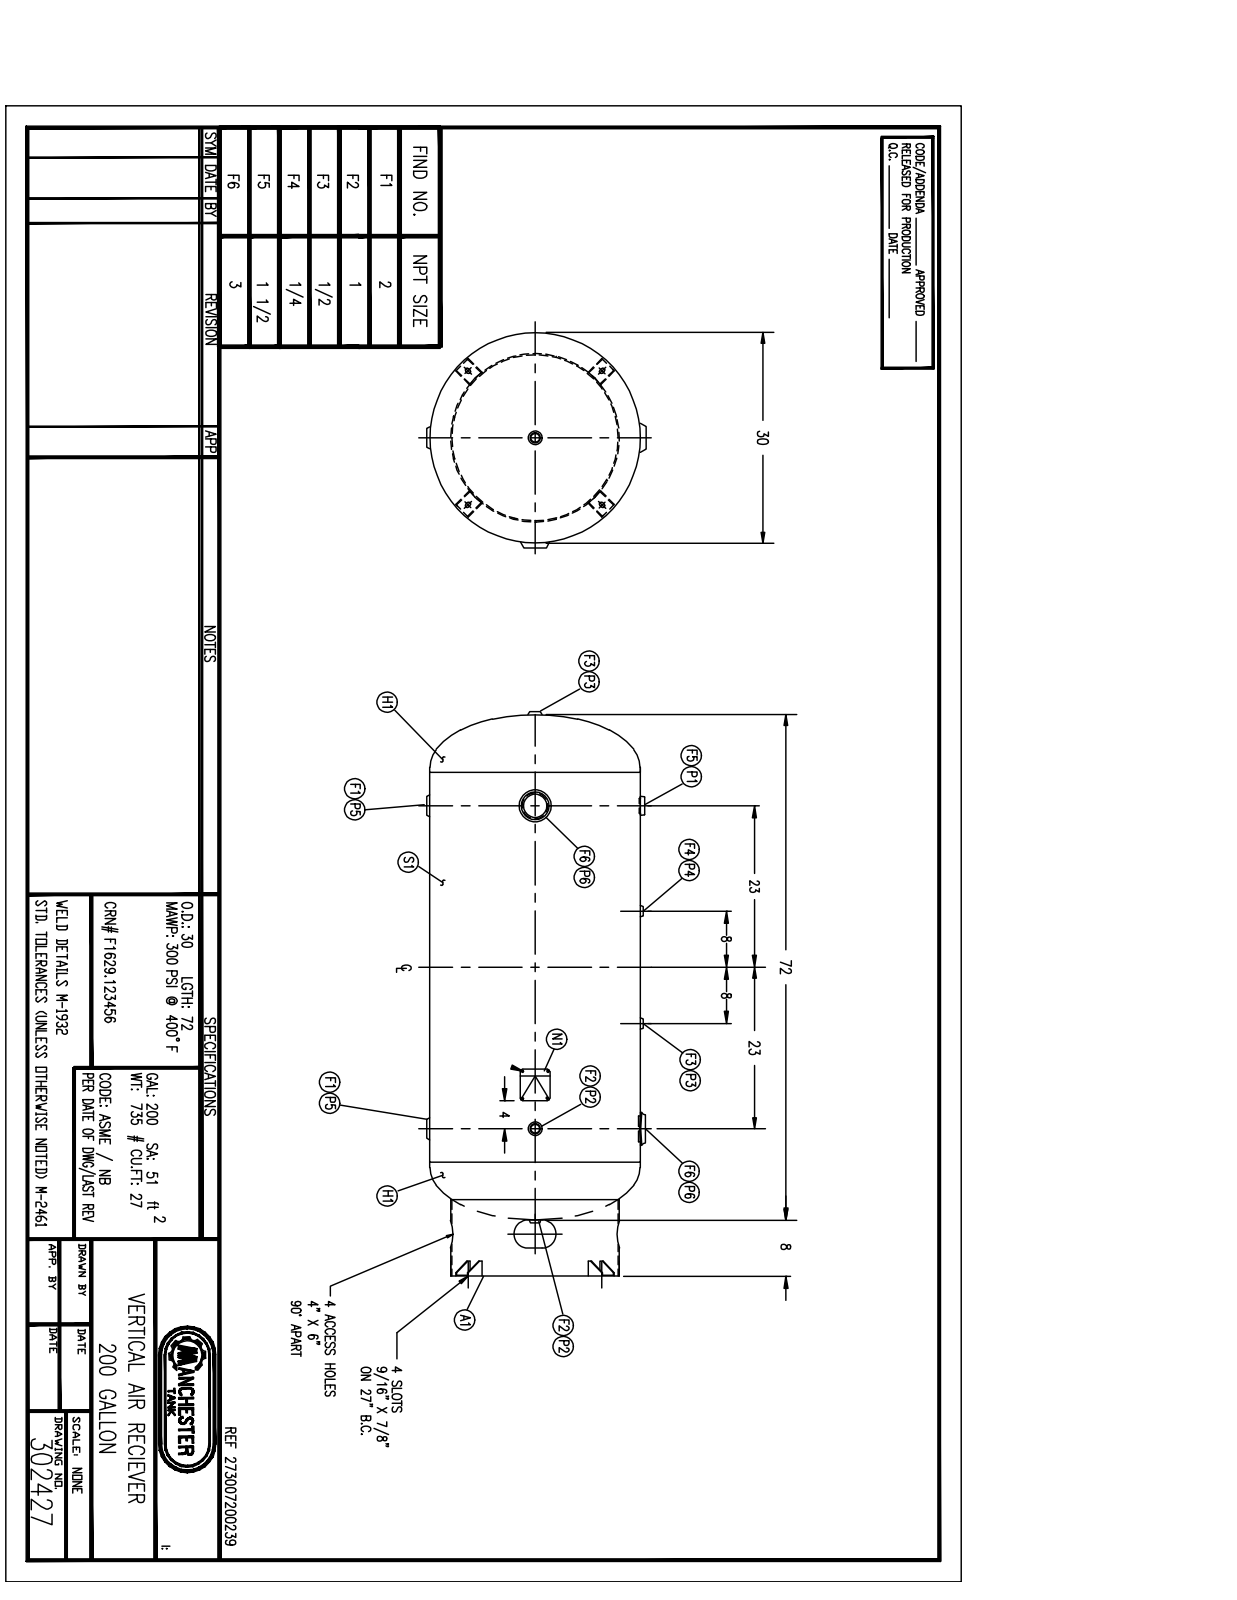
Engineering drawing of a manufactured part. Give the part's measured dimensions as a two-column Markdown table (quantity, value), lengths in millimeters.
| quantity | value |
| --- | --- |
| part name | 302427 |
| STEP written by | SolidWorks 2011 (CONFIG_CONTROL_DESIGN) |
| units | millimeters |
| bodies | 0 solids, 288 faces (105 planar, 85 cylindrical, 98 other) |
| overall size | 2043 × 804.5 × 782.6 |
| round holes (diameter × count) | 60.3 × 3, 21.3 × 2, 13.7 × 1, 25.4 × 1, 33.4 × 1, 33.4 × 1, 48.3 × 1, 600.4 × 1, 746.1 × 1 |
| round bosses / shafts (diameter × count) | 92.1 × 3, 60.3 × 2, 46.1 × 2, 762 × 1, 744.6 × 1, 609.6 × 1, 68.3 × 1, 44.5 × 1 |
| partial cylindrical surfaces (radius × count) | 6.4 × 8, 7.1 × 8, 9.8 × 8, 382.5 × 1 |
| main face-to-face distances | 427.7, 1378, 1805.6, 3.4, 60.5, 1802.2, 424.3, 3.4, 57.2, 63.9 |
| hole center spacings | 381, 787.4, 1168.4, 406.4 |
